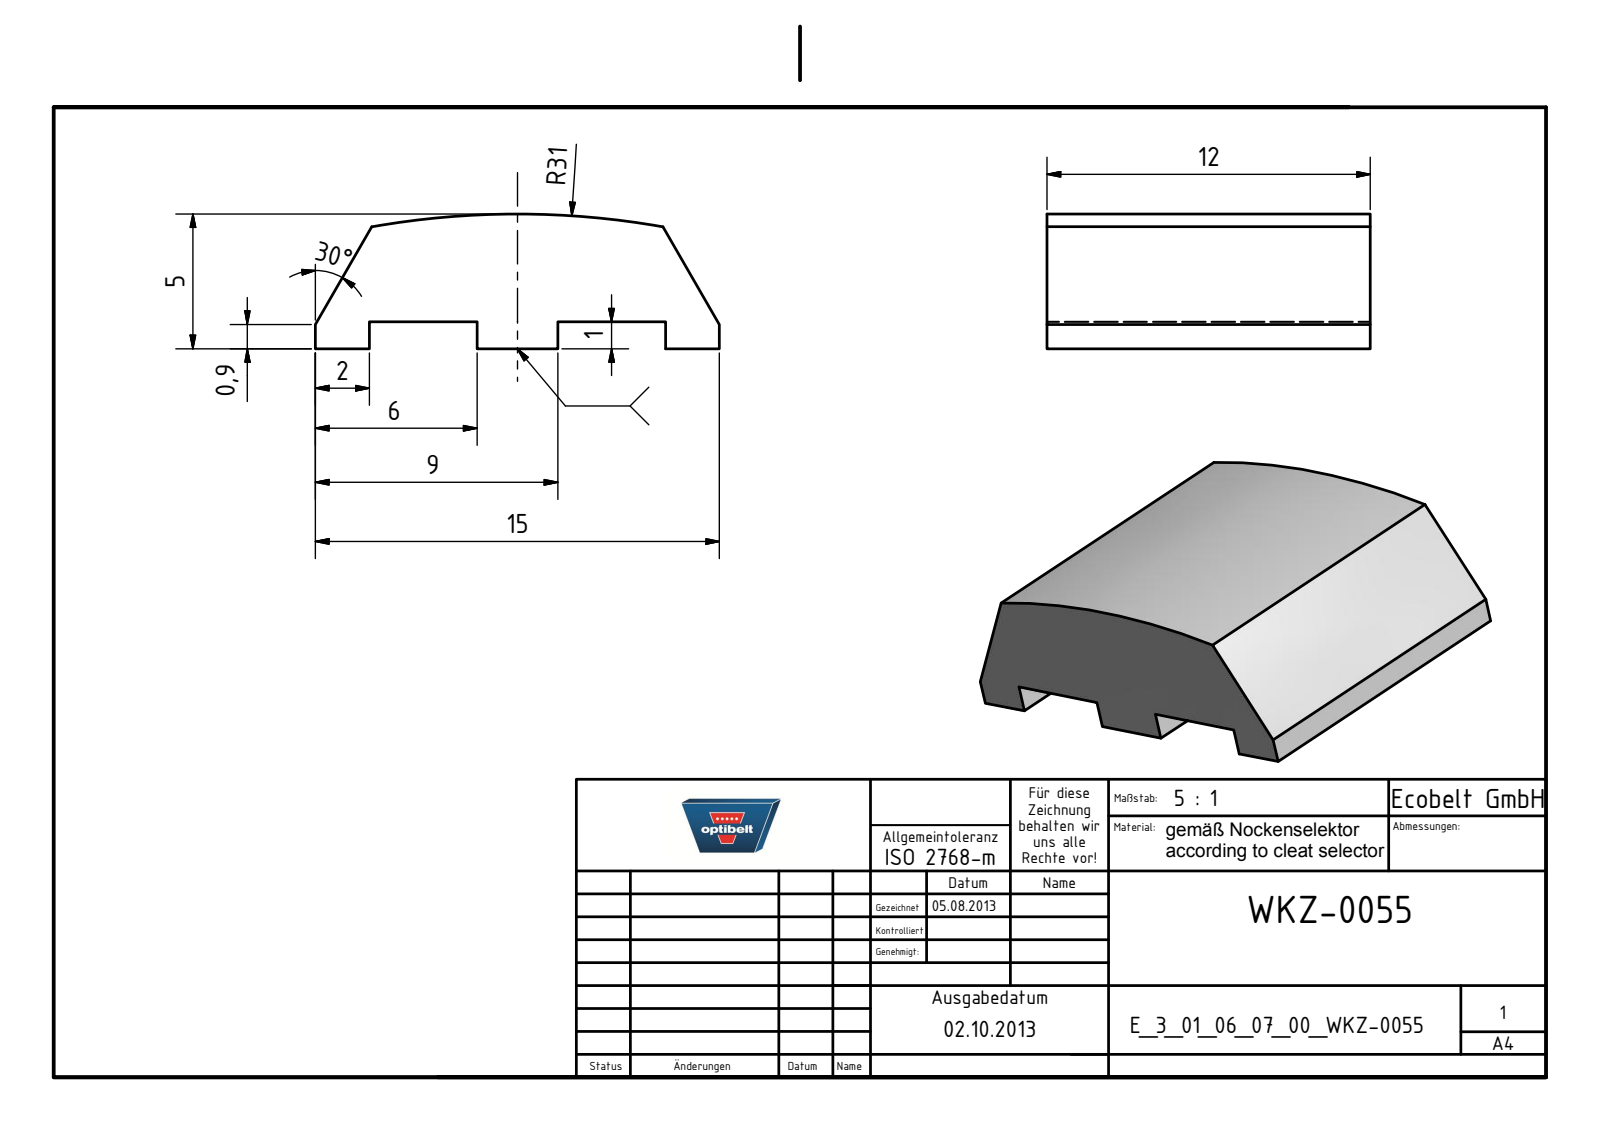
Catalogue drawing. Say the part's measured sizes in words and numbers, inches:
The part is named "E_3_01_06_07_00_WKZ-0055". Its 3-D file was written by "Autodesk Inventor 2025 (AUTOMOTIVE_DESIGN)". It is 1 solid with 16 faces: 15 planar, 1 cylindrical and 0 other. Overall it measures 0.591 by 0.472 by 0.197 inches. Its volume is 0.041 cubic inches and its surface area 0.918 square inches. Partial cylindrical surfaces (rounded edges, fillets, slot ends): 1 of radius 1.22. The main face-to-face distances are 0.039, 0.472, 0.157, 0.276, 0.079, 0.236, 0.354, 0.512, 0.118, 0.433.
